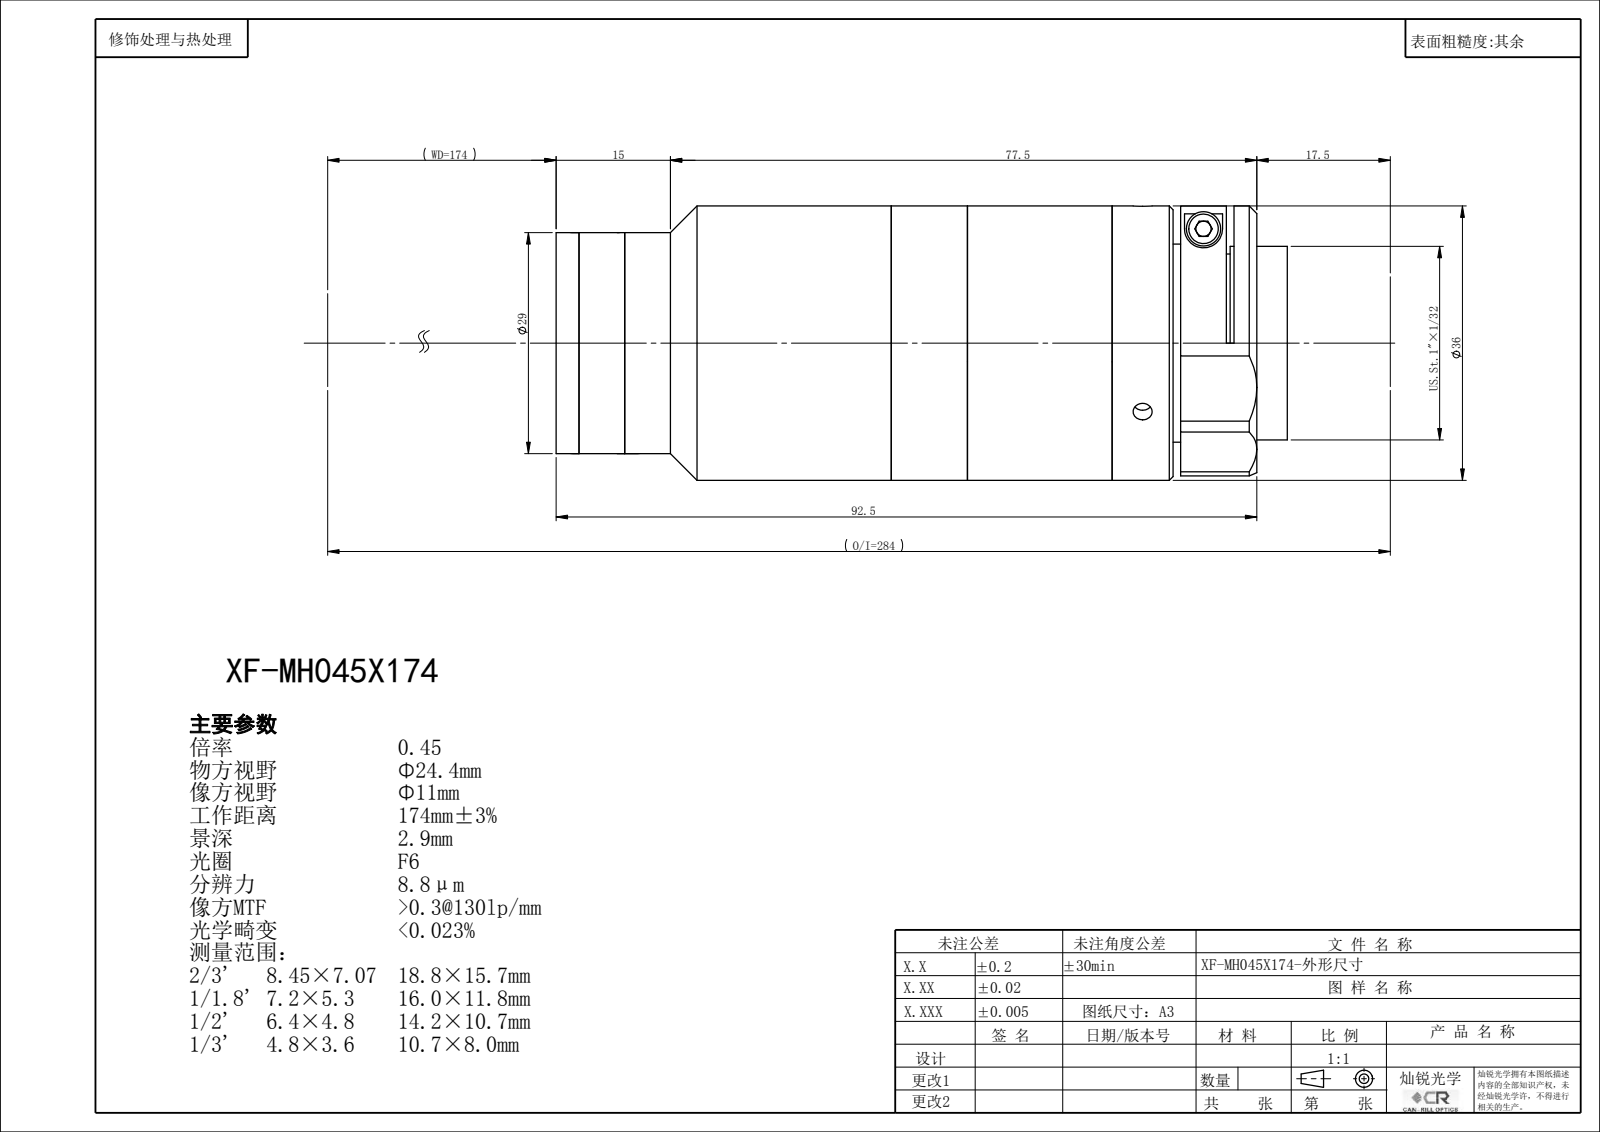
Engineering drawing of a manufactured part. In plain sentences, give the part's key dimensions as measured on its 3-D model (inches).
The part is named "XF-MH045X174". Its 3-D file was written by "SolidWorks 2022 (CONFIG_CONTROL_DESIGN)". It is 0 solids with 131 faces: 67 planar, 42 cylindrical and 22 other. Overall it measures 3.802 by 1.417 by 1.417 inches. Round holes: 3 of diameter 0.098, 1 of diameter 0.709, 1 of diameter 0.882, 1 of diameter 0.945, 1 of diameter 0.98, 1 of diameter 1.039. Round bosses or shafts: 1 of diameter 1.417, 1 of diameter 1.339, 1 of diameter 1.142, 1 of diameter 1. The main face-to-face distances are 0.771, 0.059, 0.712, 1.142, 1.854, 1.913, 0.394, 0.748, 1.46, 1.519.
